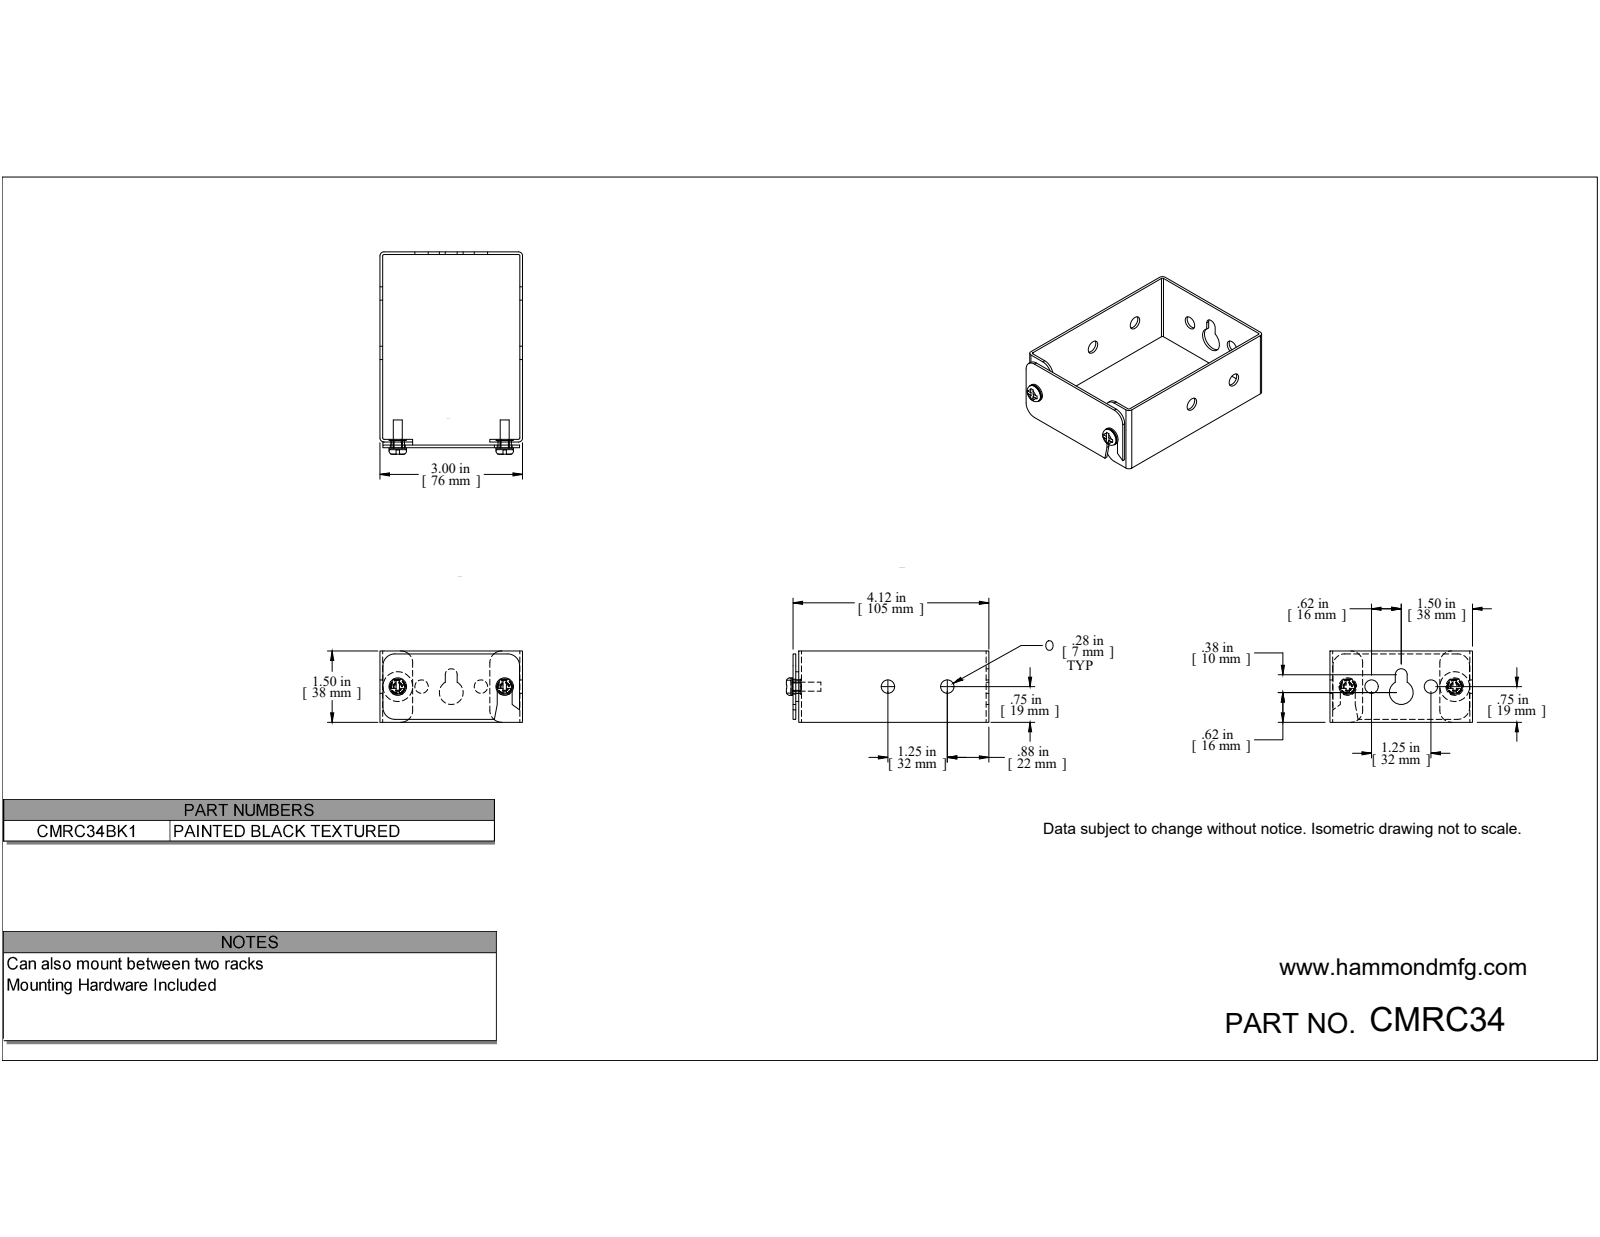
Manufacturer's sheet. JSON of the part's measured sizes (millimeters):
{"part_name": "CMRC34BK1", "step_written_by": "SolidWorks 2019 (AUTOMOTIVE_DESIGN)", "units": "millimeters", "bodies": {"solids": 8, "faces": 129, "planar": 84, "cylindrical": 41, "other": 4}, "overall_size": [108.2, 76.2, 38.1], "volume_mm3": 20730, "surface_area_mm2": 30480, "round_holes": [[7.1, 6], [4, 2], [8, 1], [8, 1], [12.7, 1]], "round_bosses_or_shafts": [[9.3, 2], [7.1, 2], [4.8, 2], [13, 1]], "partial_cylinders_radius": [[6.4, 7], [0.7, 4], [2.2, 4], [3.2, 1], [4, 1]], "face_to_face_distances": [1.4, 74.8, 103.1, 76.2, 73.3, 101.7, 104.6, 3, 100.2, 4.4], "hole_center_spacings": [12.7, 16.2, 28.8, 44.5, 31.8, 31.8, 57.2]}
